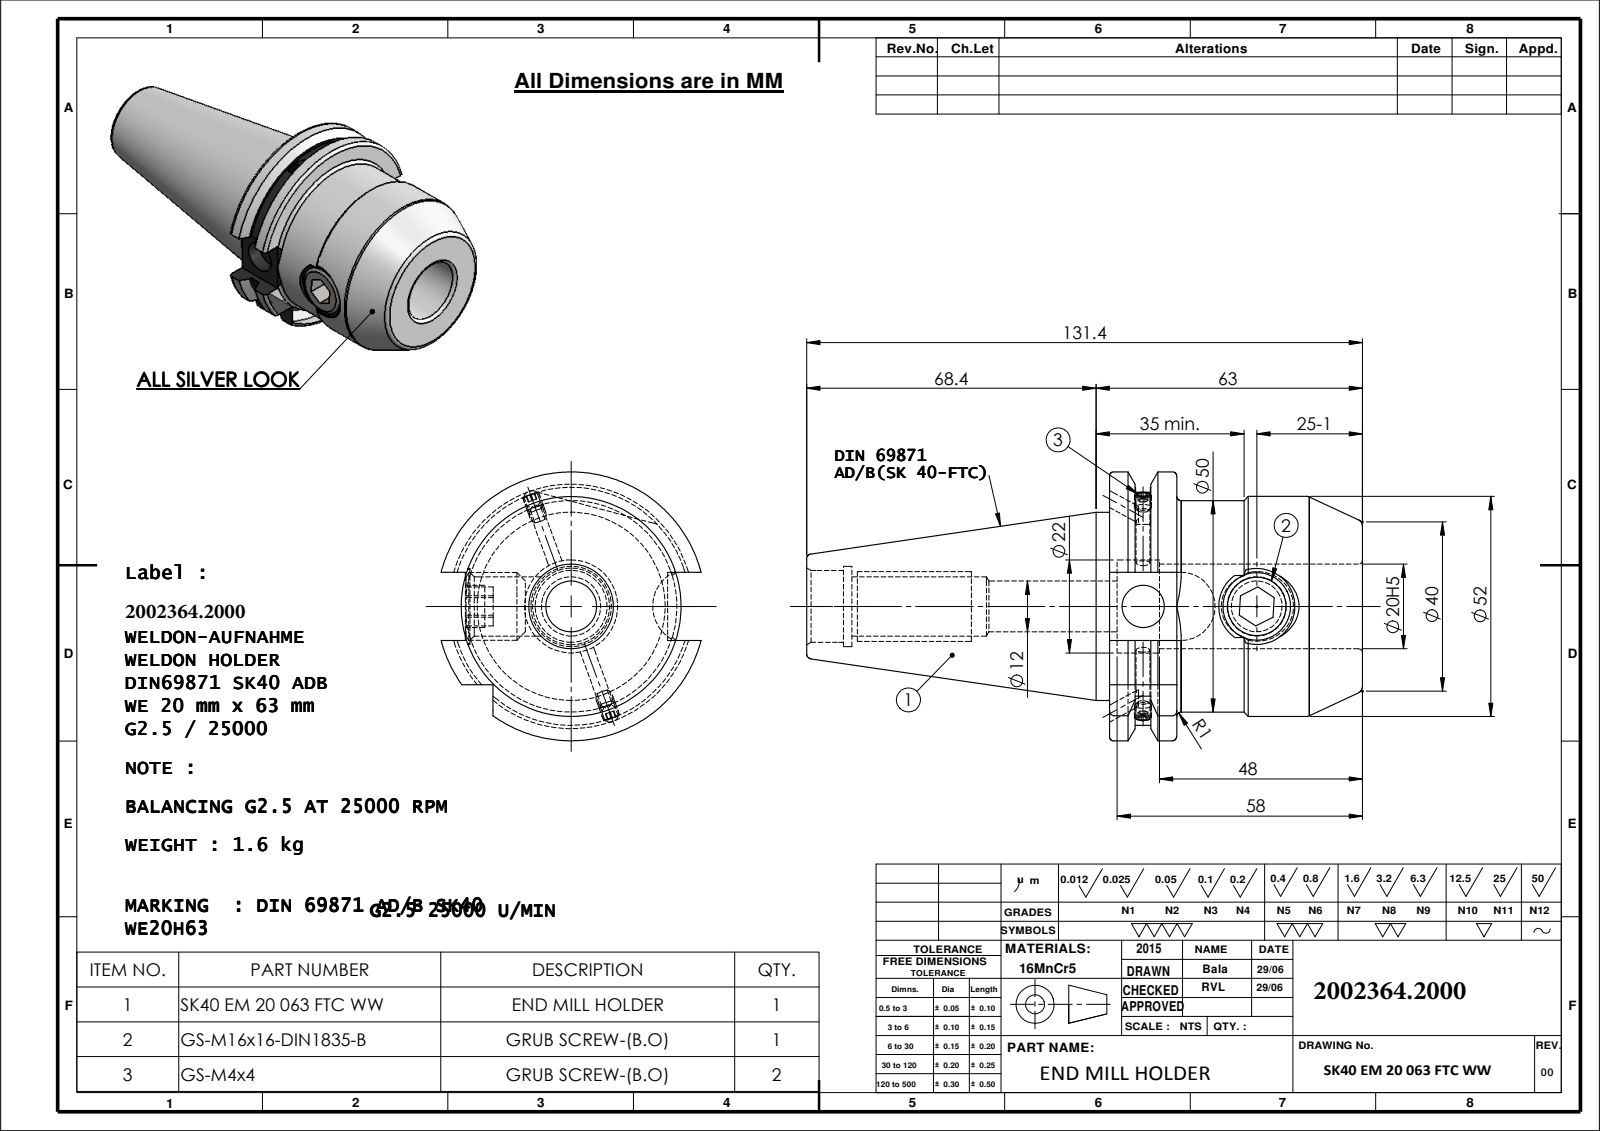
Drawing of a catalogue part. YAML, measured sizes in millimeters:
part_name: "Copy of M4X4_DIN 913 - M4 x 4-N; SK40 EM 20 063 FTC WW; 91406-WE7 20063; M16X16_ISO 4026 - M16 x 10-N"
step_written_by: "SolidWorks 2009 (CONFIG_CONTROL_DESIGN)"
units: millimeters
bodies: {solids: 4, faces: 170, planar: 60, cylindrical: 48, other: 62}
overall_size: [131.4, 63.55, 61.48]
volume: 166479
surface_area: 32406
round_holes:
  - {diameter: 14, count: 2}
  - {diameter: 3.3, count: 1}
  - {diameter: 10, count: 1}
  - {diameter: 12, count: 1}
  - {diameter: 17, count: 1}
  - {diameter: 18, count: 1}
  - {diameter: 19, count: 1}
  - {diameter: 20, count: 1}
  - {diameter: 22, count: 1}
round_bosses_or_shafts:
  - {diameter: 4, count: 2}
  - {diameter: 52, count: 1}
  - {diameter: 50, count: 1}
  - {diameter: 44.45, count: 1}
  - {diameter: 16, count: 1}
partial_cylinders:
  - {radius: 8.05, count: 1}
  - {radius: 28.12, count: 1}
  - {radius: 31.77, count: 1}
face_to_face_distances: [59.8, 15.9, 43.9, 1.8, 14.1, 58, 16.1, 47.8, 71.6, 73.4]
hole_center_spacings: [26.85]
